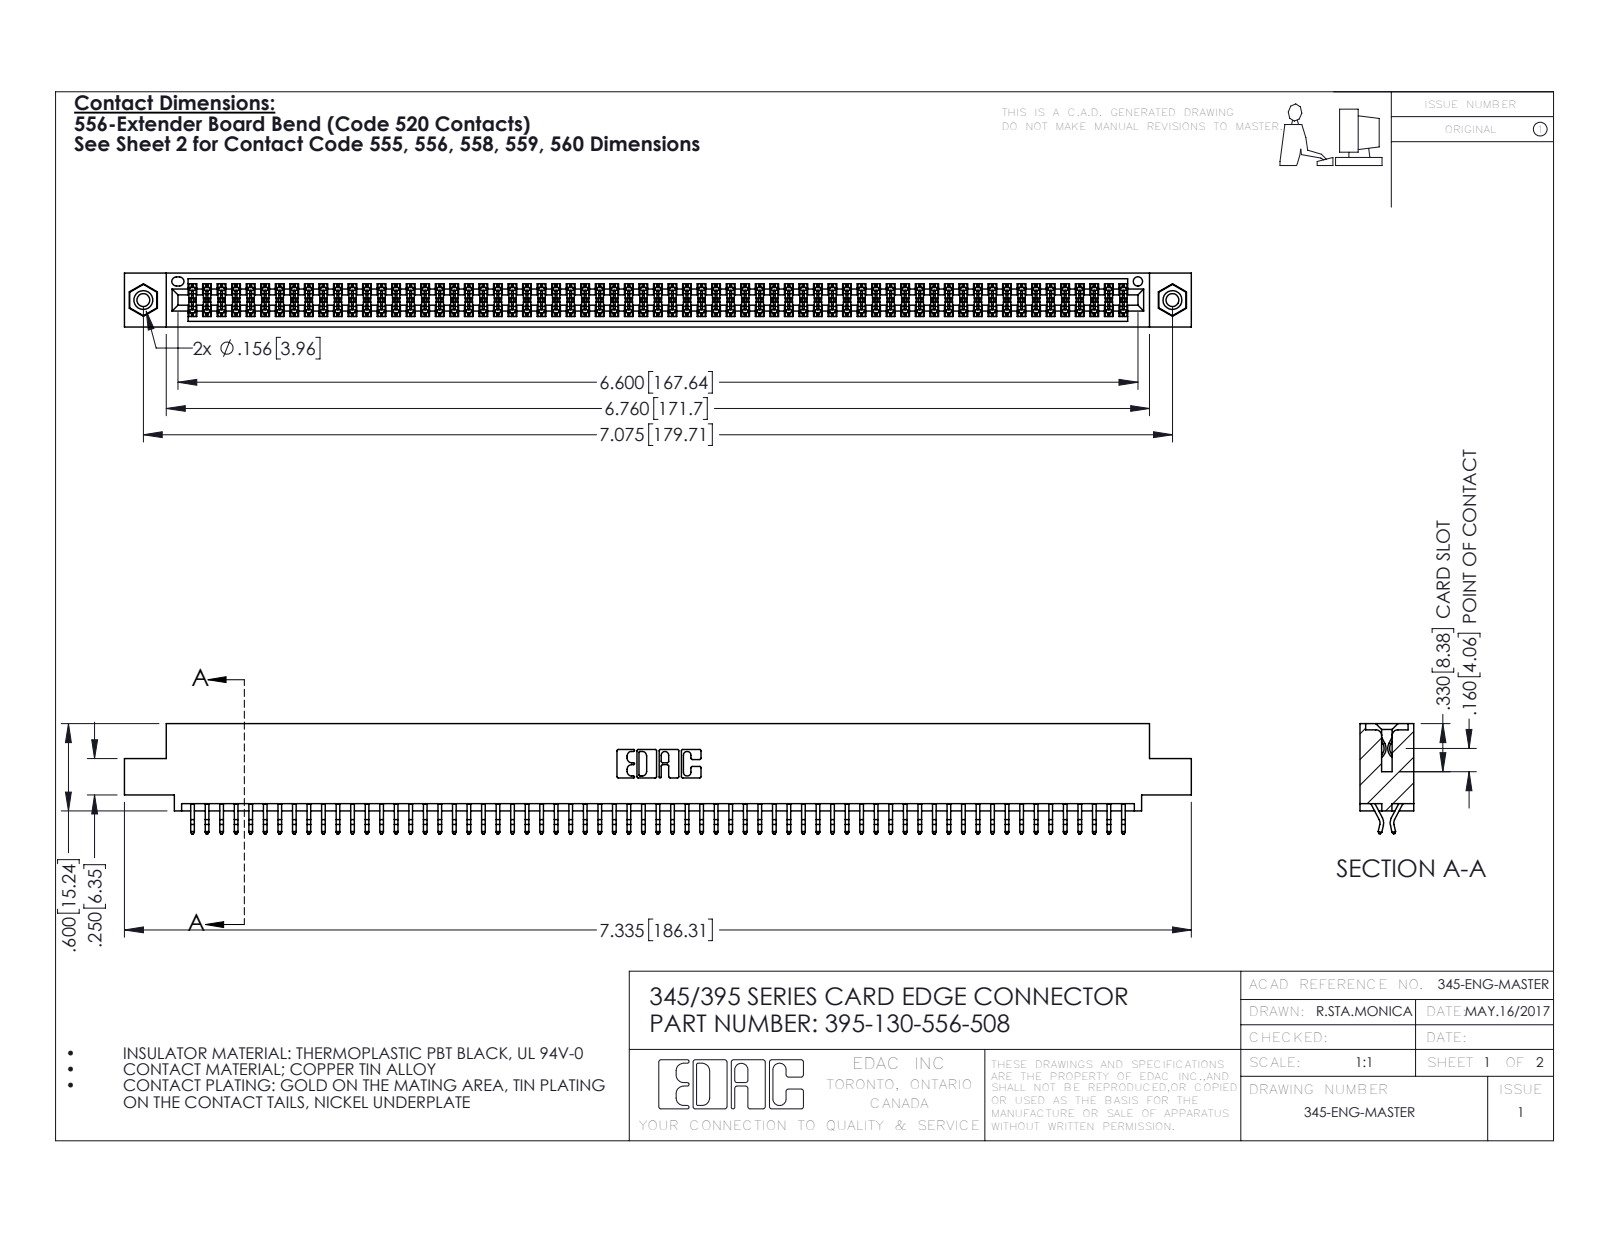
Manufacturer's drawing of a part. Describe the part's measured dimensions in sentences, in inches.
The part is named "345 Part_0.110 Offset - 0.156 Dia-TI; 395-130-556-508; 345-250-001_345-250-003-102; 345-292-001_556 Tail". Its 3-D file was written by "SolidWorks 2016 (CONFIG_CONTROL_DESIGN)". It is 133 solids with 7470 faces: 4926 planar, 2528 cylindrical and 16 other. Overall it measures 7.335 by 0.757 by 0.37 inches. Its volume is 1.112 cubic inches and its surface area 42.44 square inches. Round holes: 2 of diameter 0.089, 2 of diameter 0.125, 2 of diameter 0.156, 1 of diameter 0.064. Round bosses or shafts: 2 of diameter 0.155. Partial cylindrical surfaces (rounded edges, fillets, slot ends): 195 of radius 0.006, 22 of radius 0.01, 6 of radius 0.007, 6 of radius 0.031, 3 of radius 0.026, 2 of radius 0.01, 2 of radius 0.014, 2 of radius 0.019. The main face-to-face distances are 0.072, 0.298, 0.37, 0.2, 0.025, 0.098, 0.272, 0.225, 0.175, 0.149. The hole center spacings are 0.27, 6.839, 7.075.
